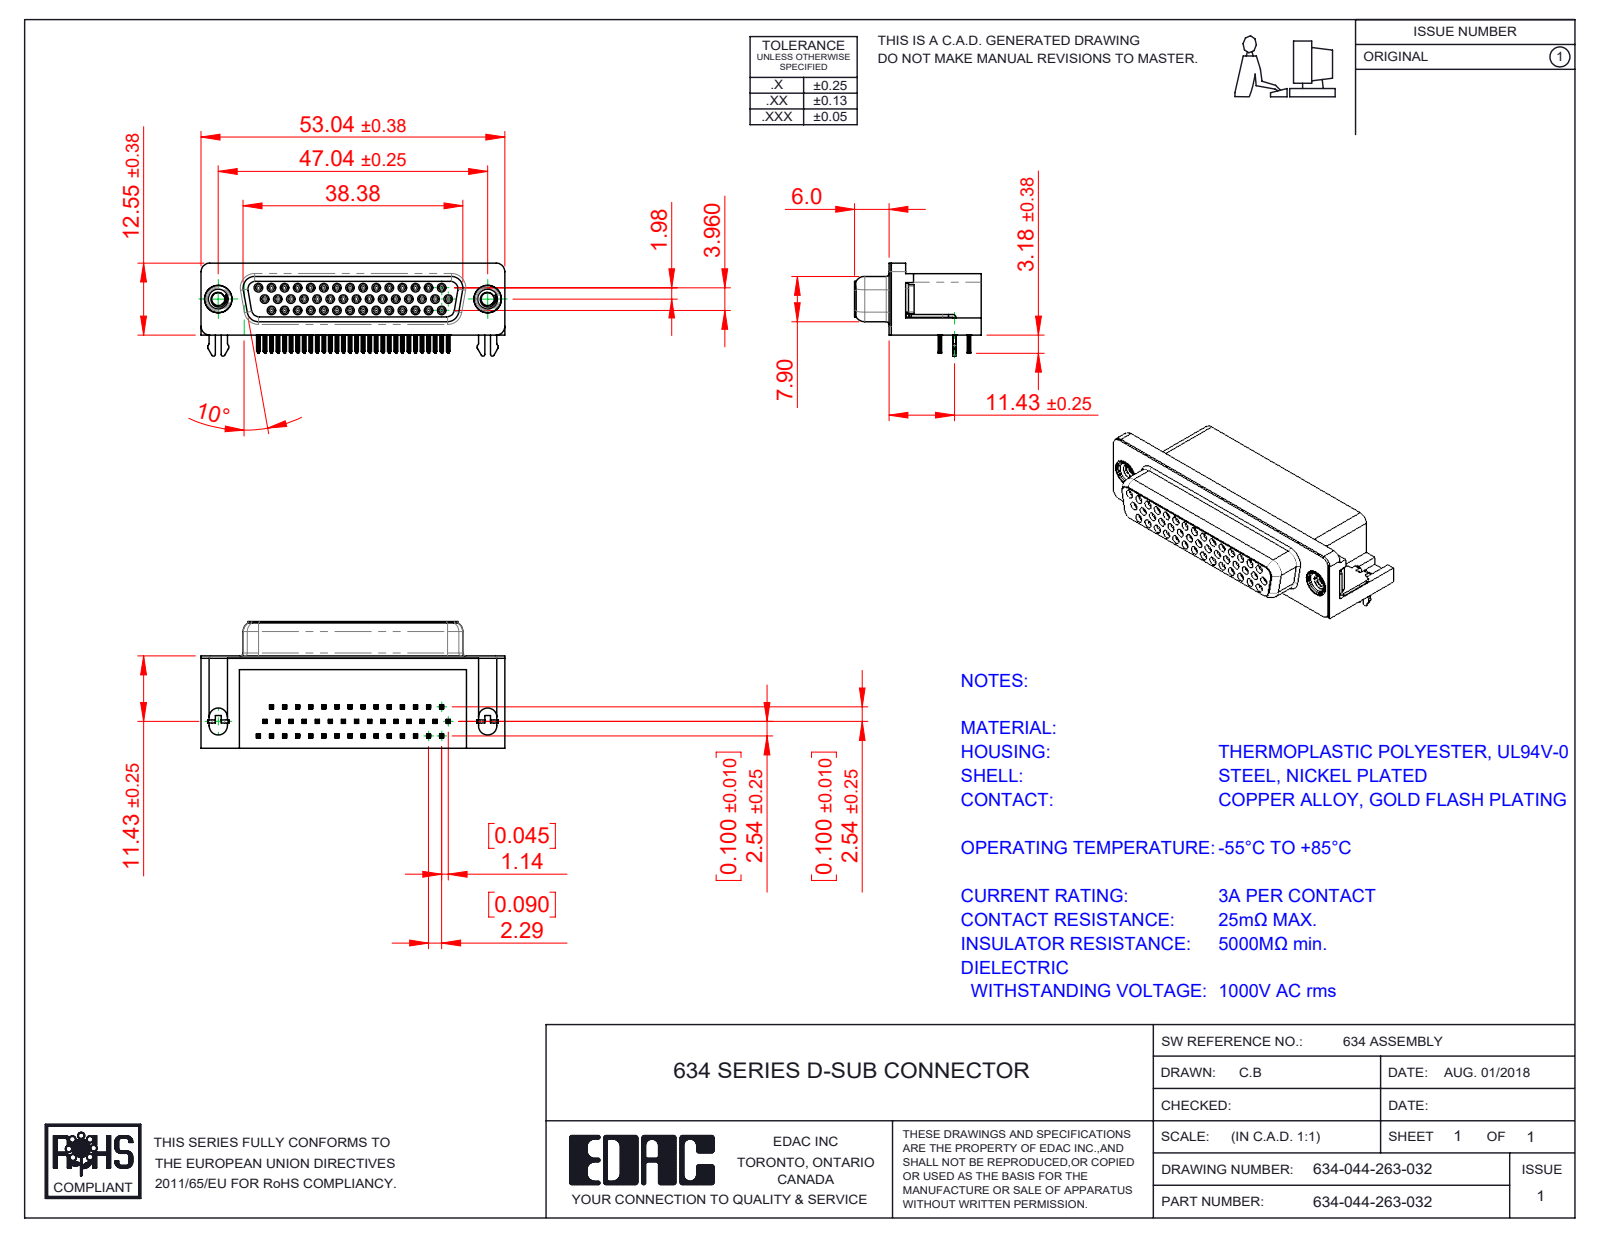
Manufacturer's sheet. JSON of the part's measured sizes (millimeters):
{"part_name": "Contact Top; 634-044-263-032; 634 Housing_44 Socket; 634 Shell_44 Socket (+4 more)", "step_written_by": "SolidWorks 2016 (CONFIG_CONTROL_DESIGN)", "units": "millimeters", "bodies": {"solids": 50, "faces": 6577, "planar": 2961, "cylindrical": 1504, "other": 2112}, "overall_size": [53.04, 22.1, 16.25], "volume_mm3": 9357, "surface_area_mm2": 13284, "round_holes": [[0.8, 44], [0.9, 44], [2.26, 2], [4, 2], [4.8, 2], [5, 2]], "round_bosses_or_shafts": [[1.2, 44], [4.9, 2], [4.75, 2], [3.9, 2]], "partial_cylinders_radius": [[0.1, 352], [0.15, 176], [0.35, 88], [0.34, 44], [1, 19], [0.28, 14], [0.5, 10], [0.25, 8]], "face_to_face_distances": [0.4, 10.35, 15.7, 7.05, 1.98, 0.85, 6.65, 0.6, 0.35, 6.4], "hole_center_spacings": [4.57, 2.29, 6.05, 11.43, 12.1, 2.27, 2.28, 4.58]}
